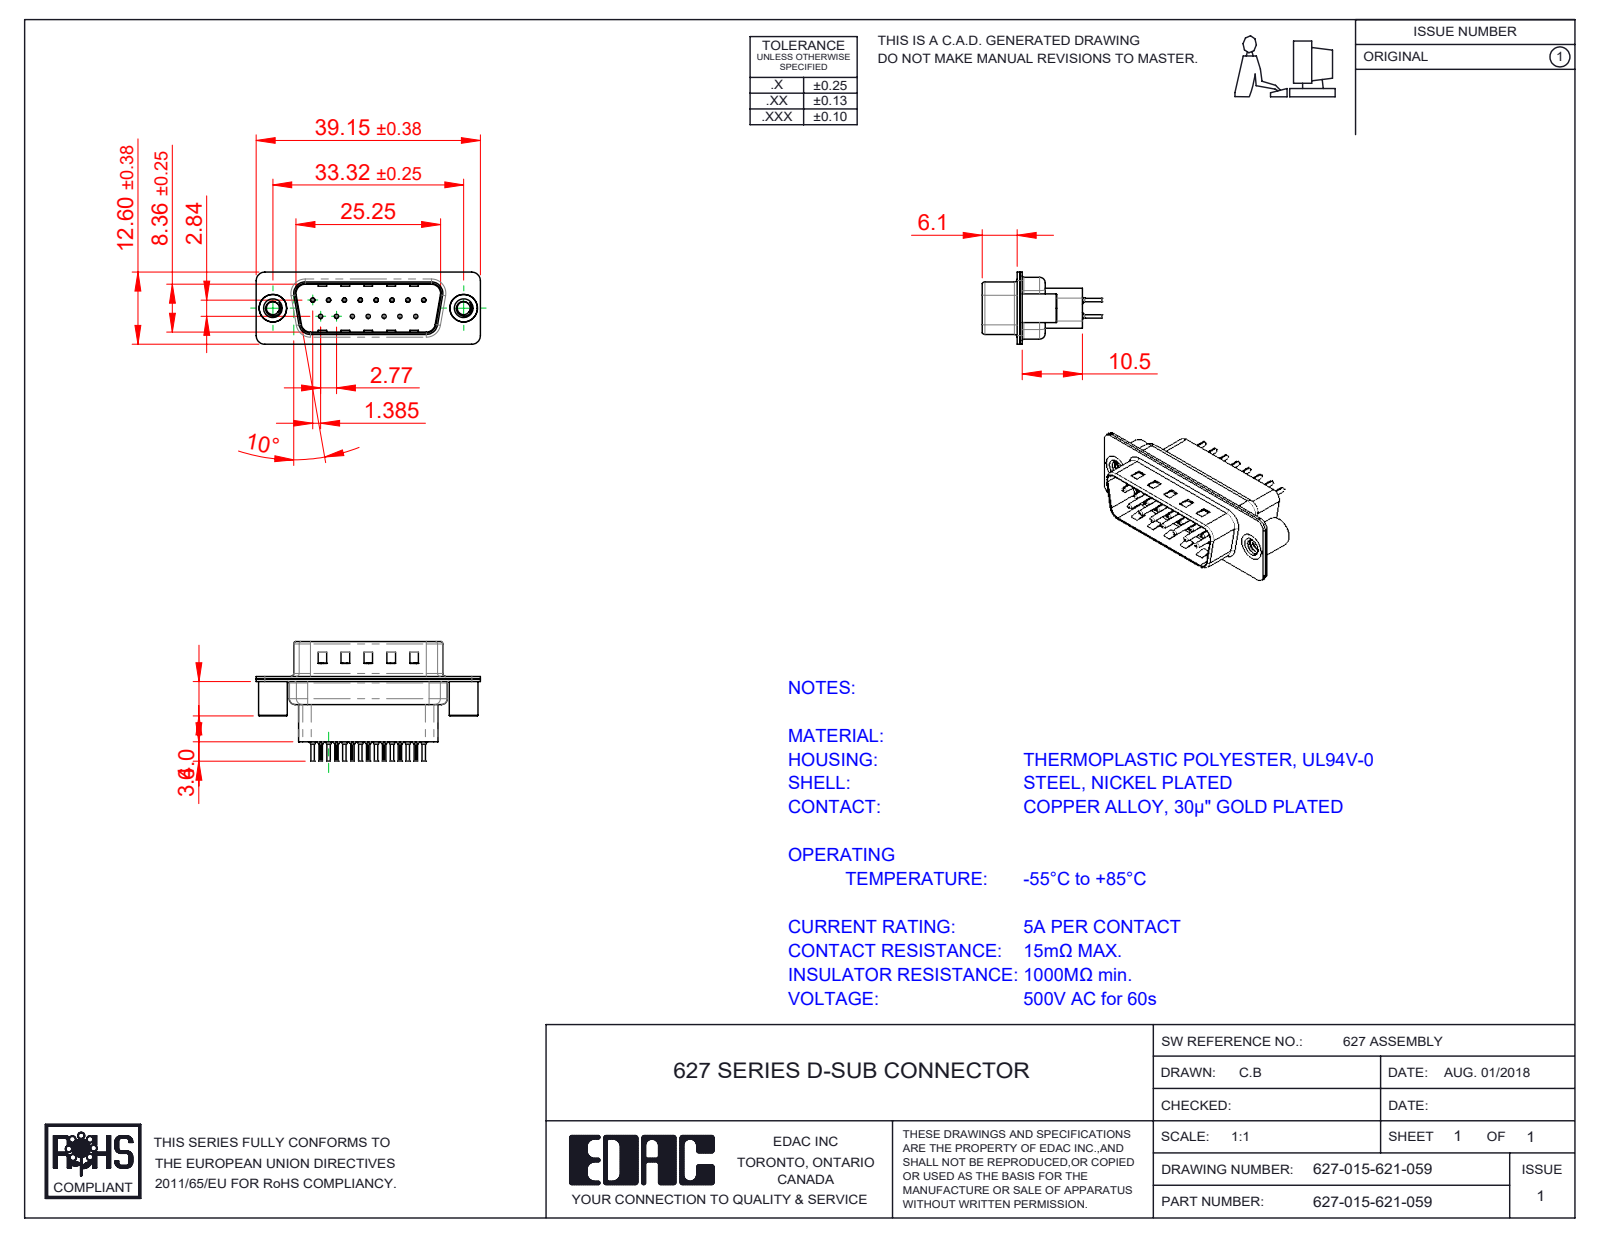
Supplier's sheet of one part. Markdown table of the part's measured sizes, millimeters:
| quantity | value |
| --- | --- |
| part name | 627 Shell Front_15 Contacts; 627 4-40 Threaded Standoff BS; 627 Shell Rear_15 Contacts; 627 Contact Row 2_21H (+3 more) |
| STEP written by | SolidWorks 2020 (CONFIG_CONTROL_DESIGN) |
| units | millimeters |
| bodies | 20 solids, 1832 faces (499 planar, 708 cylindrical, 625 other) |
| overall size | 39.15 × 20.8 × 12.6 |
| volume | 2 635 mm³ |
| surface area | 6 801 mm² |
| round holes (diameter × count) | 0.2 × 15, 0.35 × 15, 1.1 × 15, 1.6 × 15, 2.26 × 2, 4 × 2, 4.8 × 2 |
| round bosses / shafts (diameter × count) | 2 × 15, 1.5 × 15, 0.75 × 15, 0.6 × 15, 5 × 2, 4.9 × 2 |
| partial cylindrical surfaces (radius × count) | 0.1 × 30, 1.5 × 16, 2 × 12, 0.5 × 8, 1.6 × 8, 0.25 × 4, 0.6 × 4, 0.65 × 4 |
| main face-to-face distances | 0.4, 0.45, 0.9, 0.82, 9.58, 1.5, 0.68, 7.68, 1.4, 1.08 |
| hole center spacings | 3.16, 2.77, 5.54, 8.31, 11.08, 5.03, 5.04, 7.48 |
